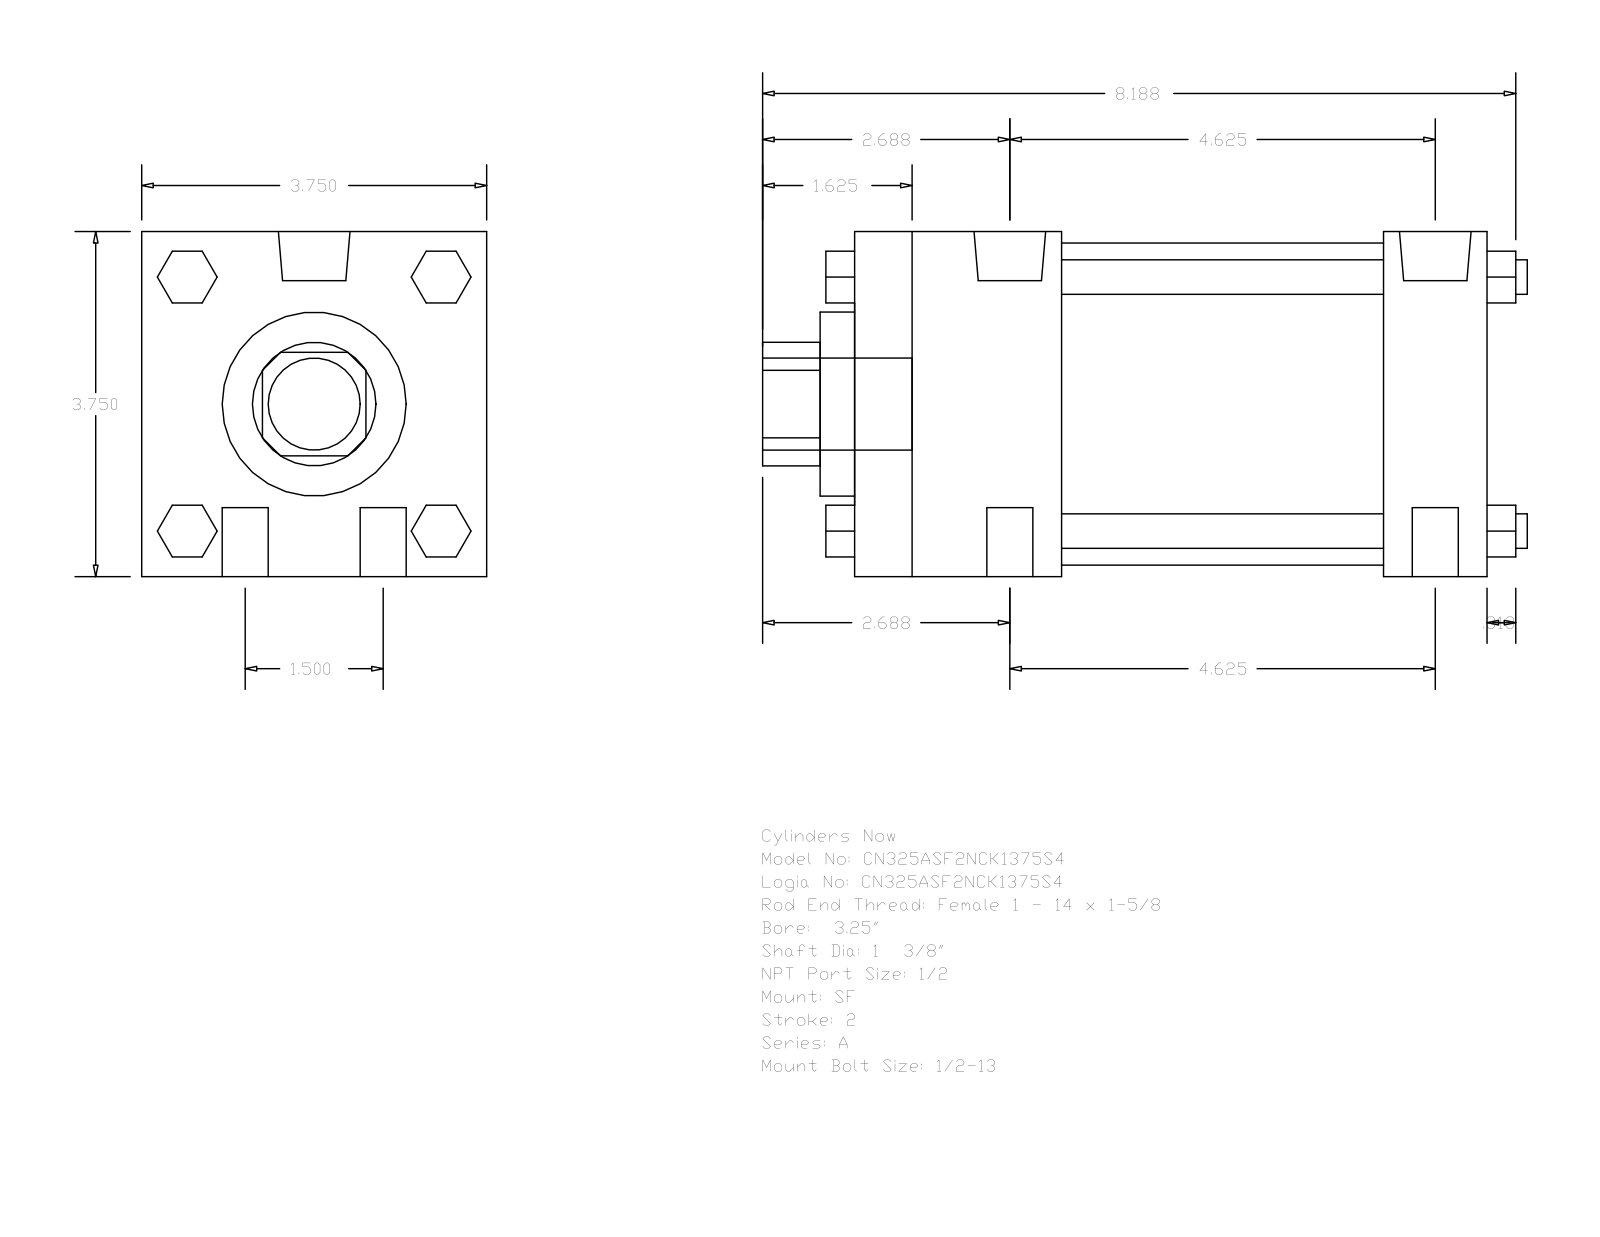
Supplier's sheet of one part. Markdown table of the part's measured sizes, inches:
| quantity | value |
| --- | --- |
| part name | A_SF__0325_1.375 |
| STEP written by | GSSL Pune (CONFIG_CONTROL_DESIGN) |
| units | inches |
| bodies | 0 solids, 124 faces (94 planar, 30 cylindrical, 0 other) |
| overall size | 8.313 × 3.75 × 3.75 |
| round holes (diameter × count) | 1.375 × 1, 2 × 1, 3.5 × 1 |
| round bosses / shafts (diameter × count) | 0.5 × 4, 0.375 × 4, 0.778 × 2, 0.344 × 2, 1 × 1 |
| partial cylindrical surfaces (radius × count) | 0.672 × 1 |
| main face-to-face distances | 3.75, 6.875, 1.125, 5.75, 2.25, 3.5, 4.625, 0.375, 2.625, 6.125 |
